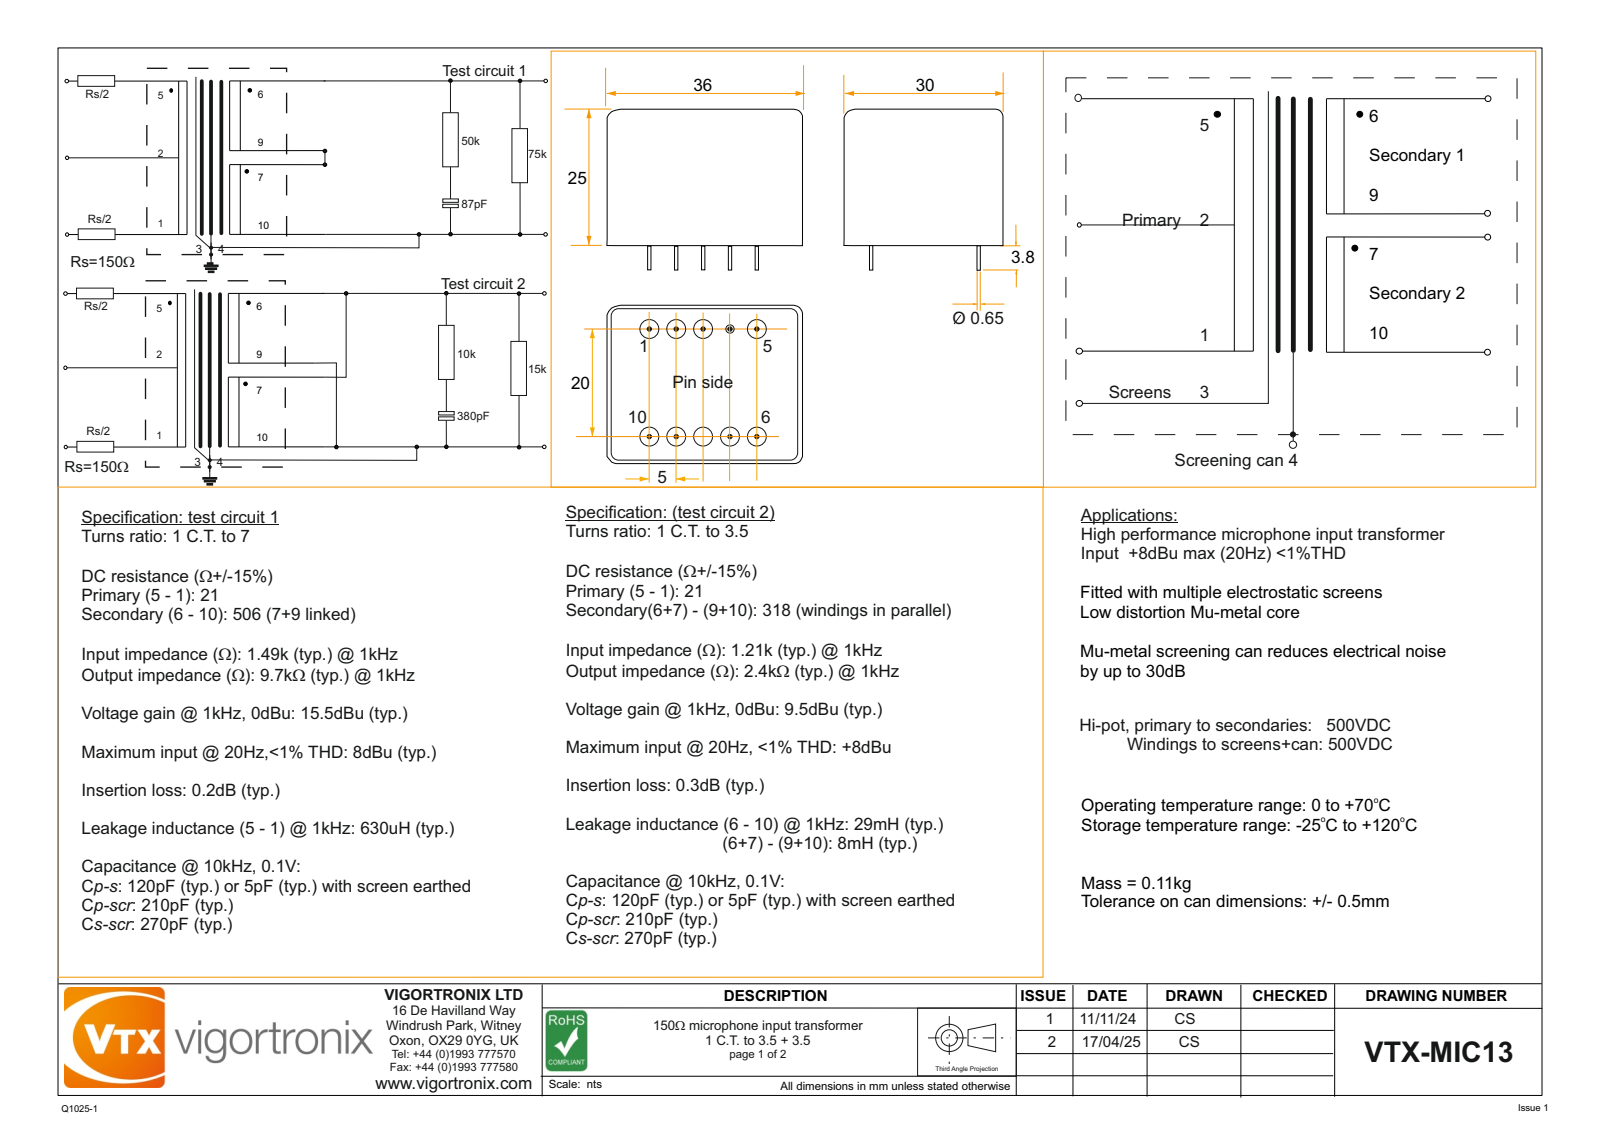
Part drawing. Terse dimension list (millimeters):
name: VTX-MIC13 Lid; VTX-MIC13; VTX-MIC13 Can; VTX-MIC13 BOBBIN
written by: SolidWorks 2024 (AUTOMOTIVE_DESIGN)
unit: mm
bodies: 3 solids, 110 faces (32 planar, 66 cylindrical, 12 other)
size: 36 × 30 × 28.8
volume: 20 336 mm³; area: 13 961 mm²
holes: 9× ⌀2.4, 1× ⌀1.5
bosses: 9× ⌀0.65
rounds: 8× R1, 8× R2.3, 8× R3, 4× R2.5
face distances: 0.7, 0.5, 3.2, 2.7, 23.2, 22.7, 20, 1.1, 24.3, 23.8
hole spacings: 5, 20.62, 20, 10, 22.36, 15, 25, 28.28
